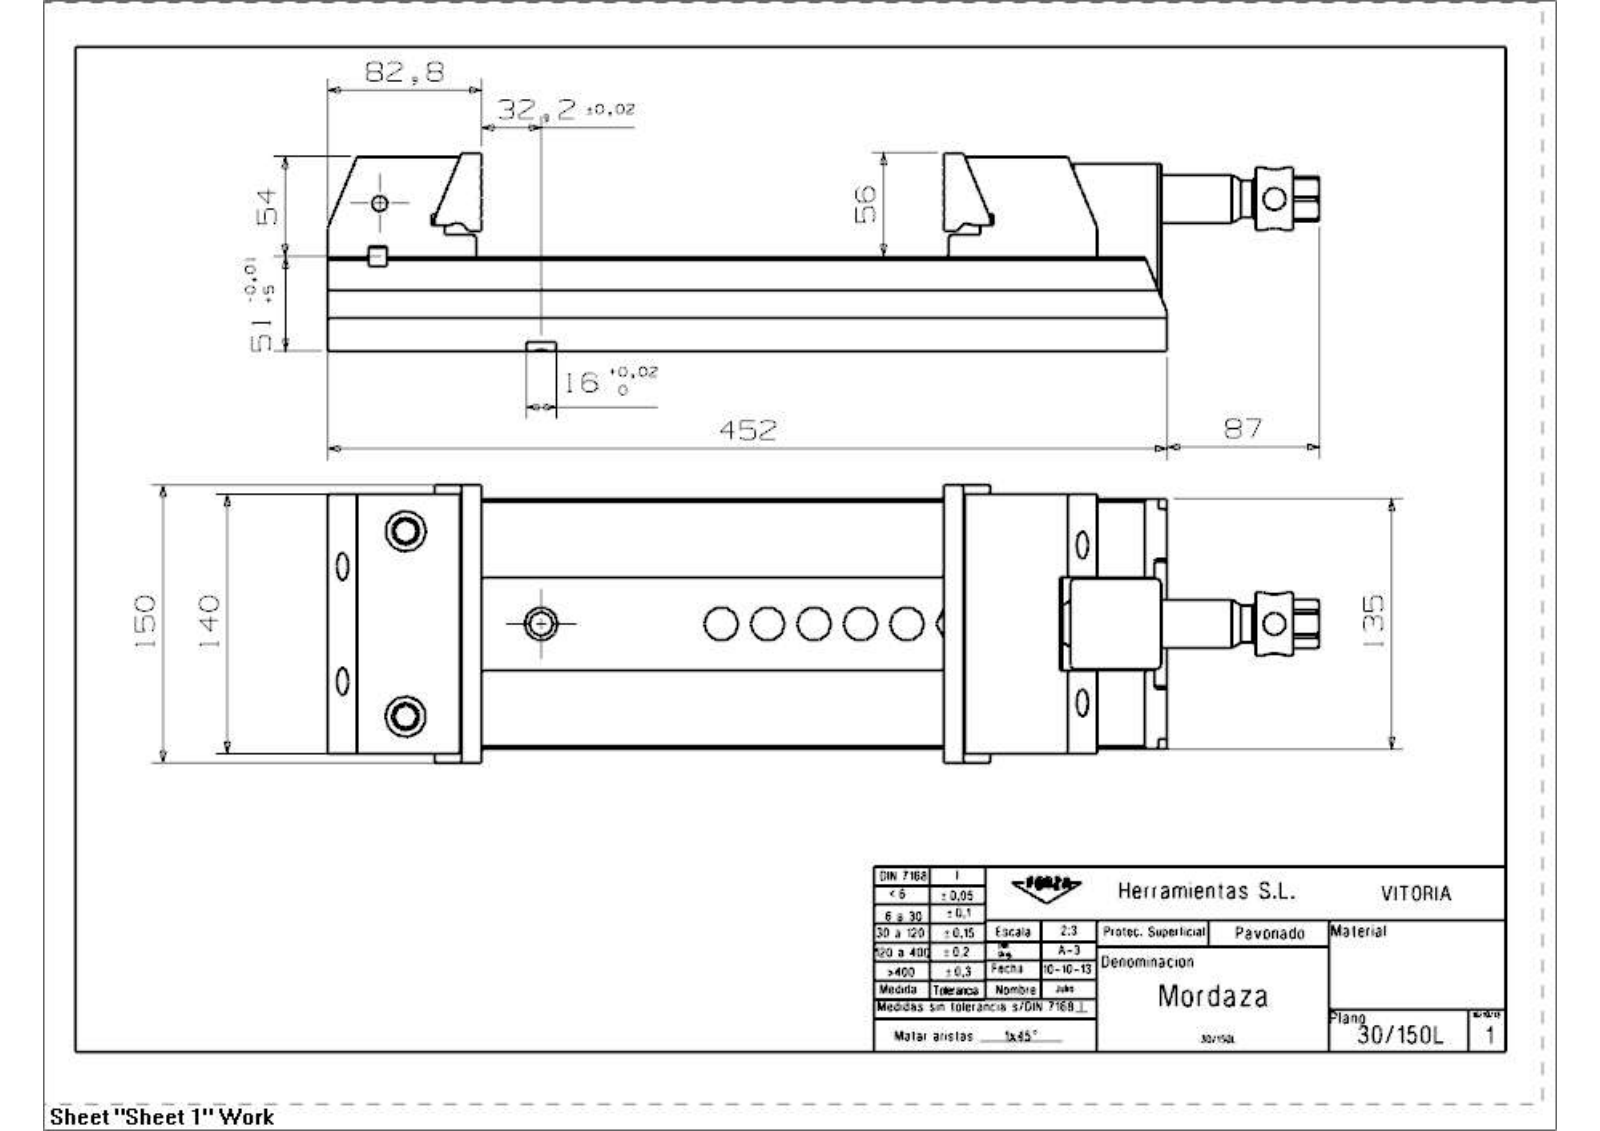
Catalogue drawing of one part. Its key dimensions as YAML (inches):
part_name: "30_150L_Mordaza"
step_written_by: "SIEMENS PLM Software NX 7.5 (CONFIG_CONTROL_DESIGN)"
units: inches
bodies: {solids: 12, faces: 435, planar: 283, cylindrical: 98, other: 54}
overall_size: [21.024, 5.906, 4.213]
volume: 208.4
surface_area: 733.8
round_holes:
  - {diameter: 0.512, count: 6}
  - {diameter: 0.591, count: 6}
  - {diameter: 0.204, count: 5}
  - {diameter: 0.275, count: 4}
  - {diameter: 0.335, count: 4}
  - {diameter: 0.346, count: 4}
  - {diameter: 0.394, count: 4}
  - {diameter: 0.417, count: 4}
  - {diameter: 0.748, count: 4}
  - {diameter: 0.472, count: 2}
  - {diameter: 0.487, count: 2}
  - {diameter: 0.709, count: 2}
round_bosses_or_shafts:
  - {diameter: 1.339, count: 1}
  - {diameter: 1.331, count: 1}
  - {diameter: 1.024, count: 1}
  - {diameter: 0.787, count: 1}
  - {diameter: 0.65, count: 1}
partial_cylinders:
  - {radius: 0.059, count: 4}
  - {radius: 0.315, count: 4}
  - {radius: 0.787, count: 4}
  - {radius: 0.063, count: 2}
  - {radius: 0.217, count: 2}
  - {radius: 0.236, count: 2}
  - {radius: 0.157, count: 1}
  - {radius: 0.354, count: 1}
face_to_face_distances: [2.008, 4.134, 0.76, 1.248, 1.063, 1.378, 0.063, 0.697, 1.945, 3.374]
hole_center_spacings: [3.747, 0.453, 2.894, 3.346, 0.455, 0.457, 0.877, 1.102]
